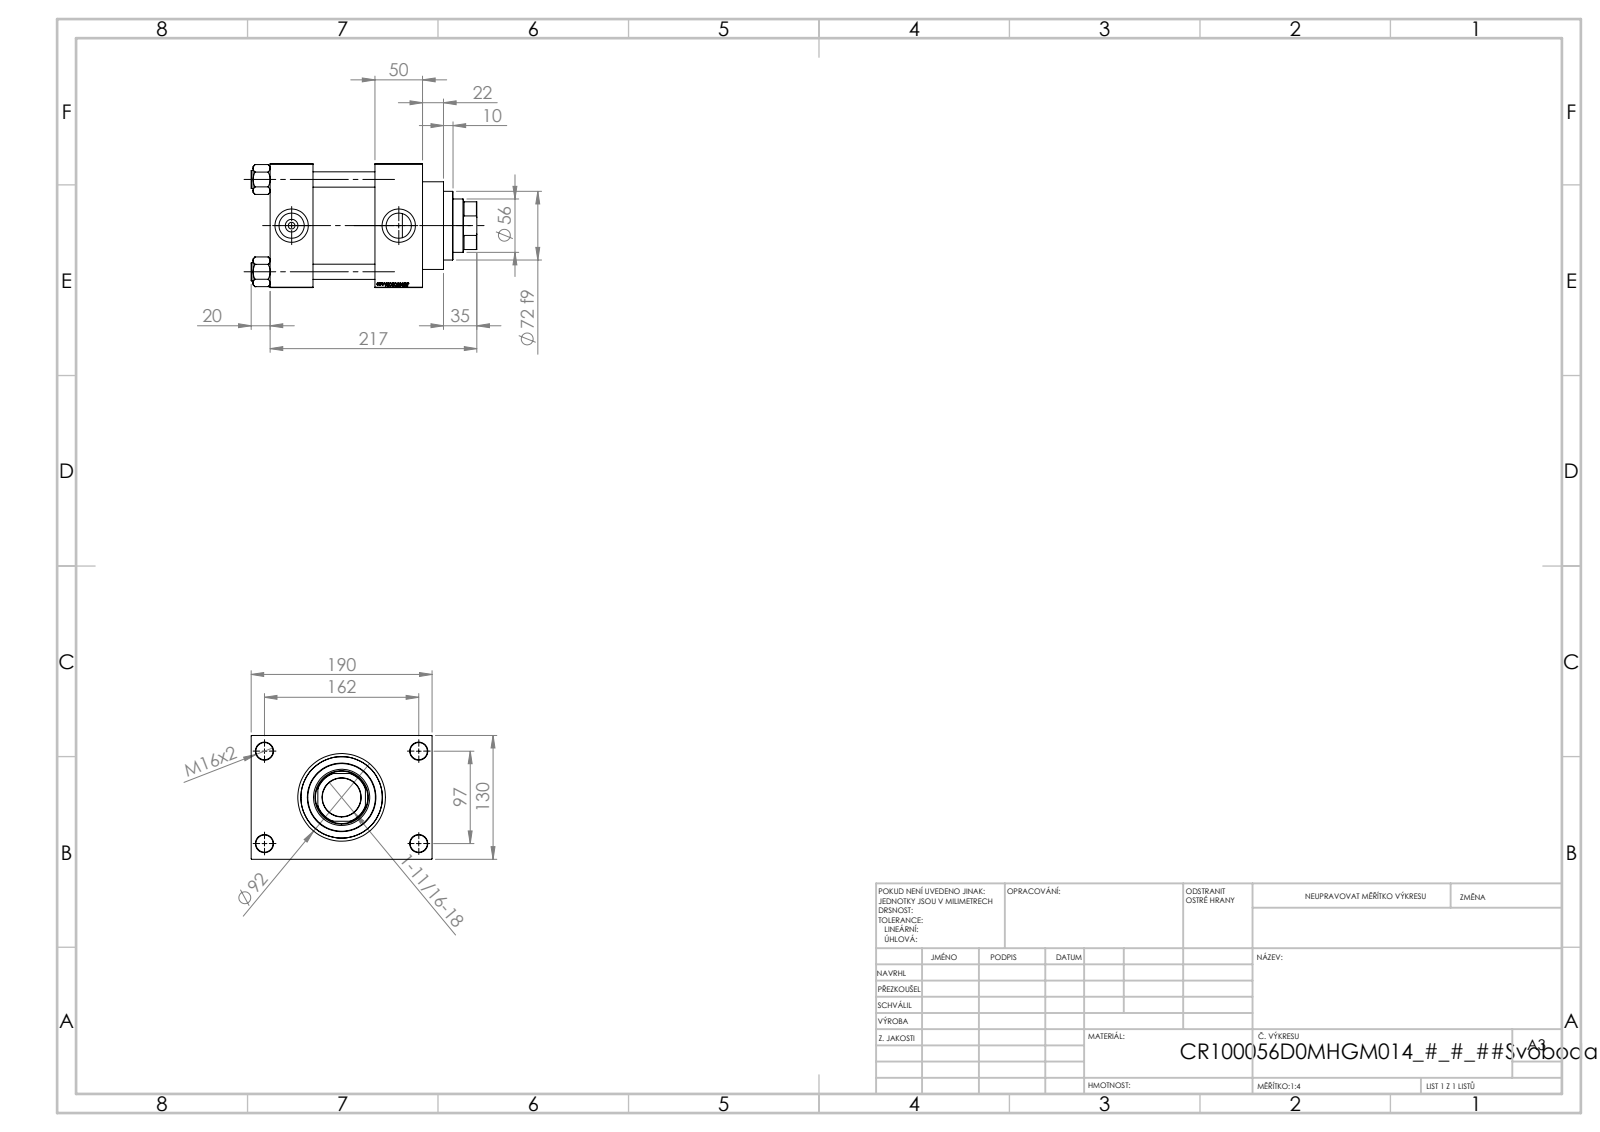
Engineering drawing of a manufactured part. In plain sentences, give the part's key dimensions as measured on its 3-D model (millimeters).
The part is named "V215CR_VCP_D; V215CR_D_TYCINKA; NUT_M5_D; V215_VC_A (+1 more)". Its 3-D file was written by "SolidWorks 2019 (CONFIG_CONTROL_DESIGN)". It is 11 solids with 1151 faces: 545 planar, 88 cylindrical and 518 other. Overall it measures 237 by 190 by 130 millimeters. Its volume is 2 603 000 cubic millimeters and its surface area 356 218 square millimeters. Round holes: 4 of diameter 16, 4 of diameter 18, 2 of diameter 7, 2 of diameter 26.44, 2 of diameter 35, 1 of diameter 40.5, 1 of diameter 56, 1 of diameter 59, 1 of diameter 76, 1 of diameter 85.5, 1 of diameter 100. Round bosses or shafts: 4 of diameter 19, 1 of diameter 106, 1 of diameter 92, 1 of diameter 72. Partial cylindrical surfaces (rounded edges, fillets, slot ends): 1 of radius 27. The main face-to-face distances are 160, 130, 65, 50, 45, 110, 115, 30, 96, 14. The hole center spacings are 32.55, 68.52, 94.41, 96.9, 102.27, 129.45, 161.73, 97.
